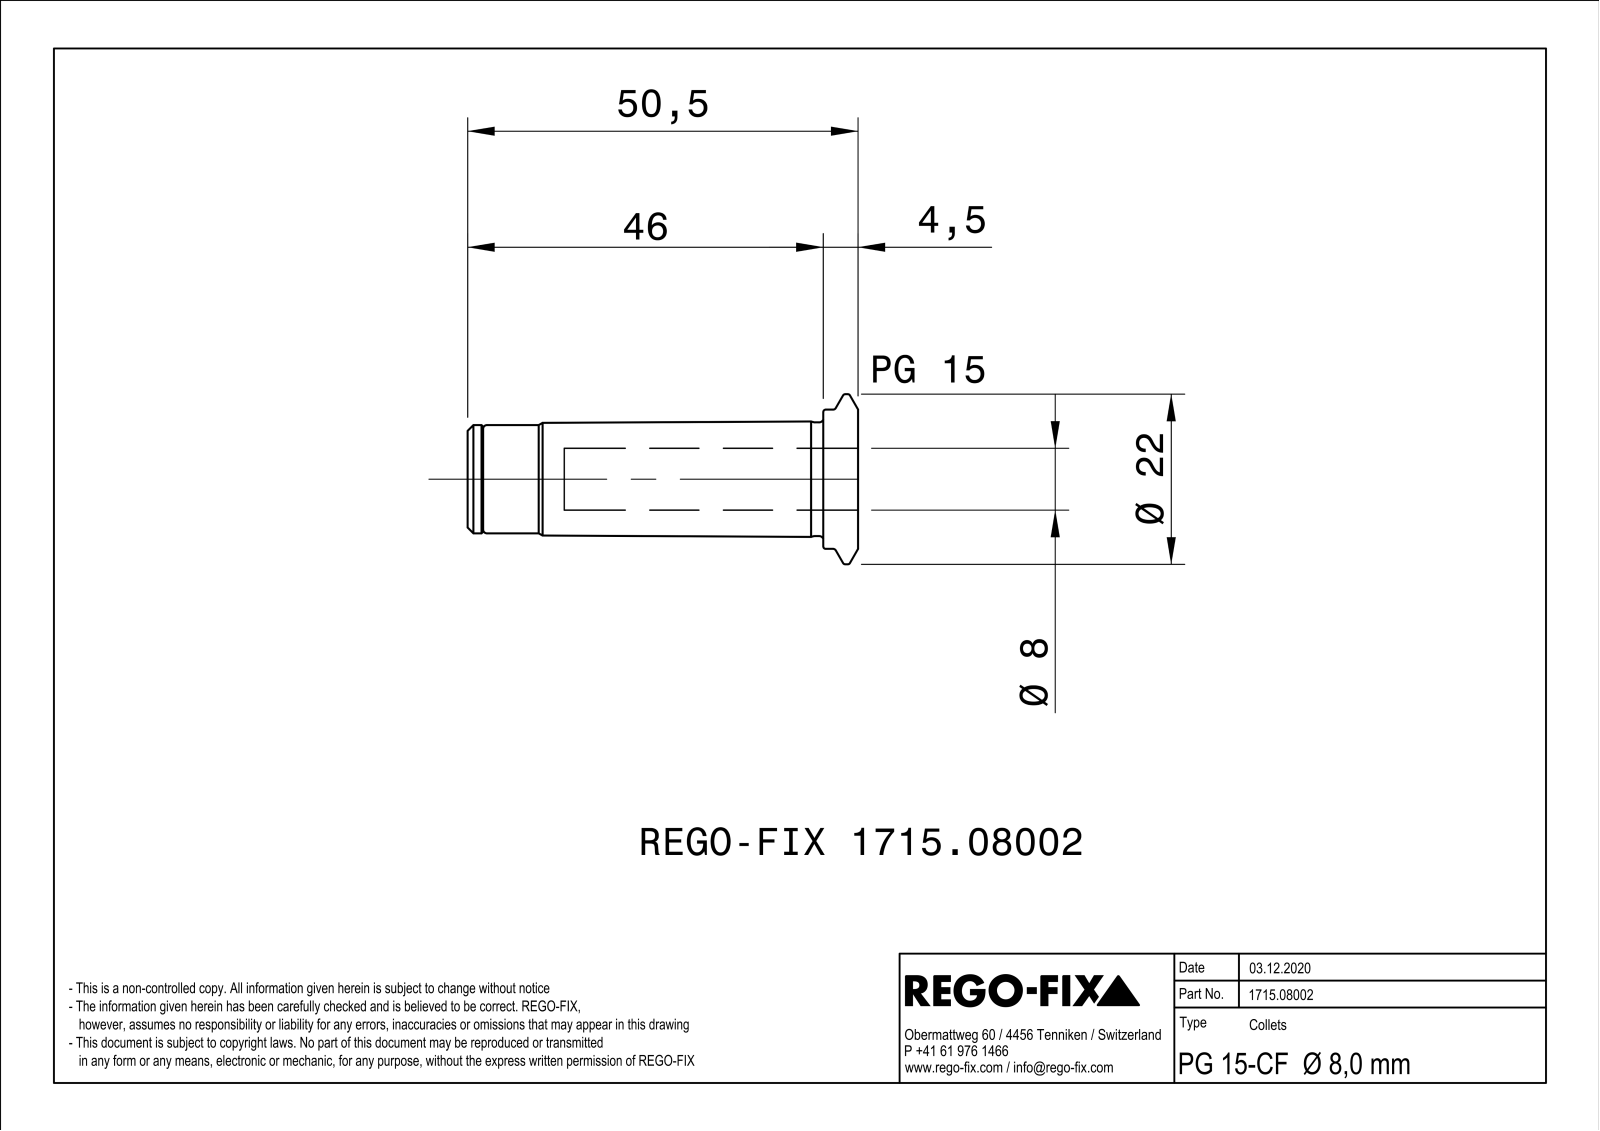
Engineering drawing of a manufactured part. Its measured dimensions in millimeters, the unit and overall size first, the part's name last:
Units: millimetres
Overall size (bounding box): 50.5 × 22 × 21.99
Round holes (diameter × count): ⌀5.2 ×1, ⌀6.92 ×1, ⌀8 ×1, ⌀8.2 ×1, ⌀10.92 ×1, ⌀12.2 ×1
Round bosses / shafts (diameter × count): ⌀22 ×1, ⌀18 ×1, ⌀14.7 ×1, ⌀14 ×1
Partial cylindrical surfaces — rounded edges, fillets, slot ends (radius × count): R0.5 ×3, R5.2 ×1, R6 ×1
Main face-to-face distances: 1, 2, 50.5, 40.5, 10, 41.5, 9, 3, 4.5, 36
Volume: 6 052 mm³ · Surface area: 5 354 mm²
Bodies: 1 solid, 120 faces (41 planar, 30 cylindrical, 49 other)
Part name (STEP PRODUCT): NOCUT
STEP written by: SIEMENS PLM Software Solid Edge ST10 (AUTOMOTIVE_DESIGN)
